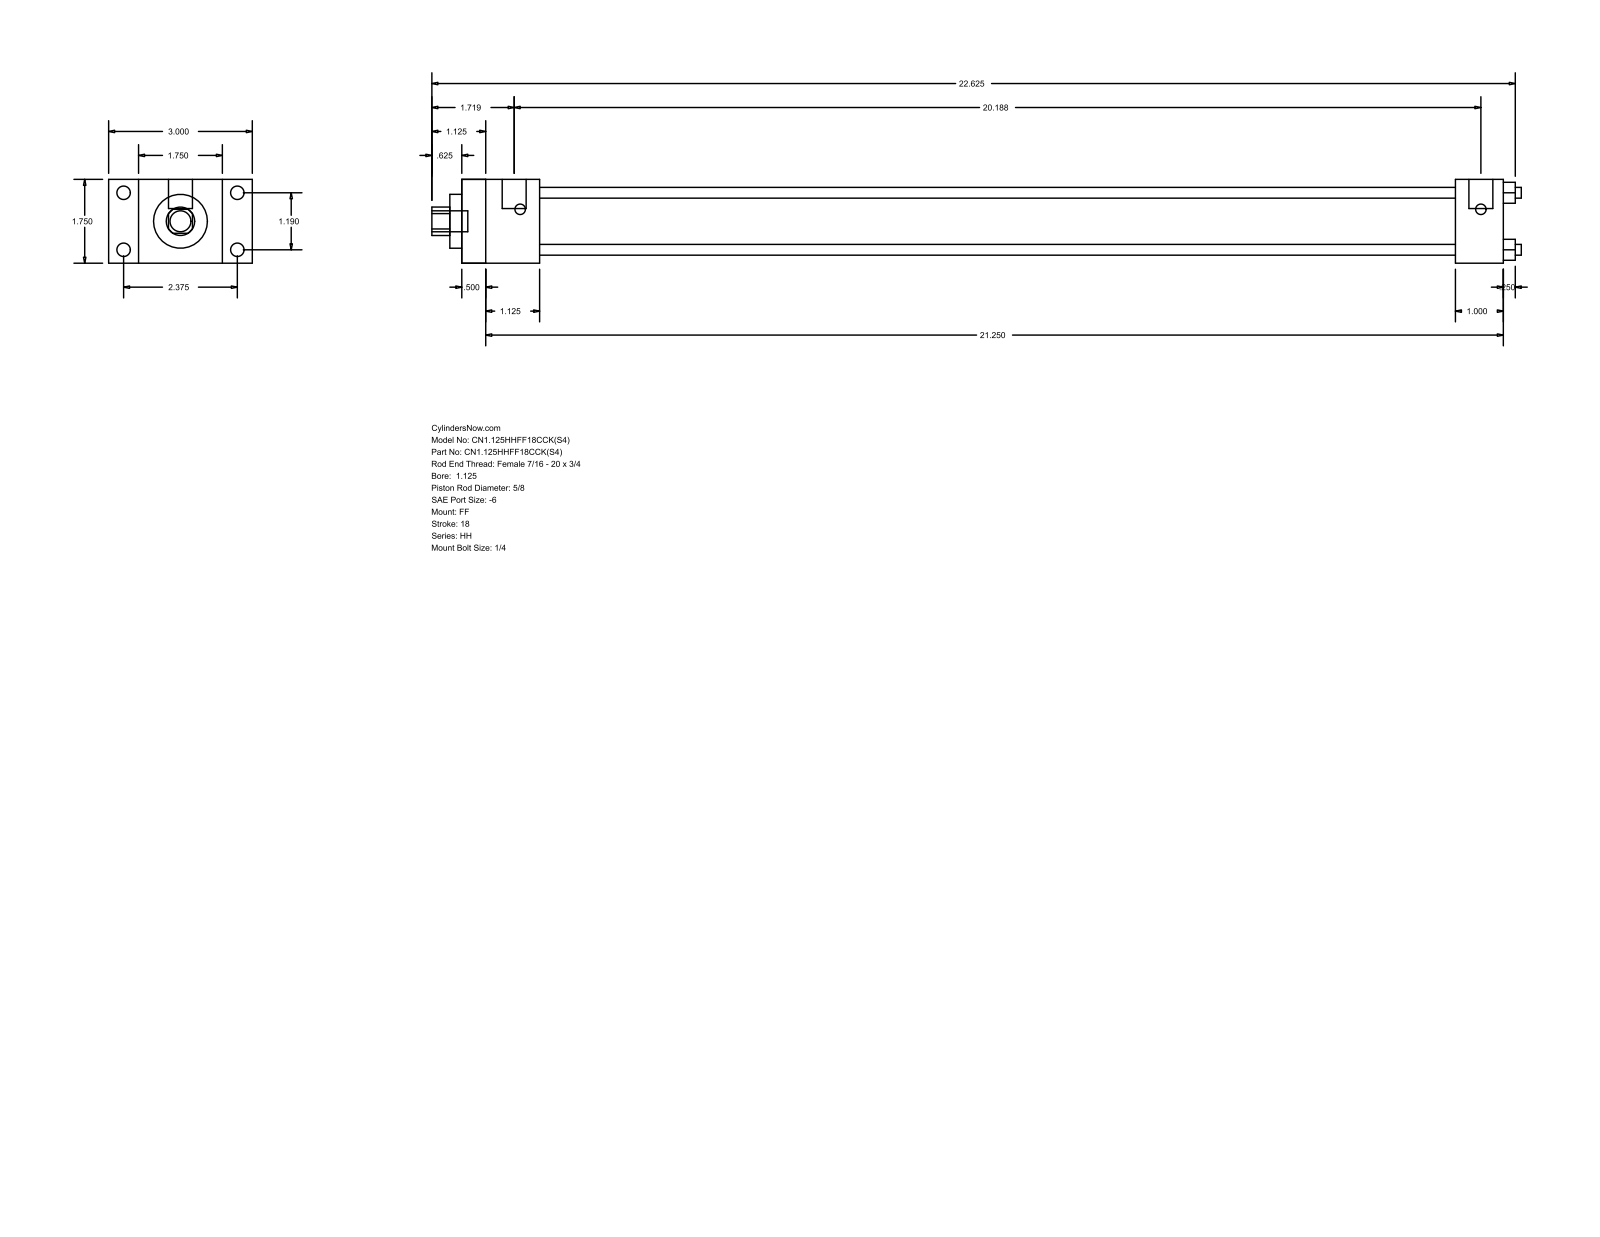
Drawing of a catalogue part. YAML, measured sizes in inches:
part_name: "HH_FF__0112_0.625"
step_written_by: "GSSL Pune (CONFIG_CONTROL_DESIGN)"
units: inches
bodies: {solids: 0, faces: 92, planar: 64, cylindrical: 28, other: 0}
overall_size: [22.75, 3, 1.75]
round_holes:
  - {diameter: 0.225, count: 4}
  - {diameter: 0.625, count: 1}
  - {diameter: 1.125, count: 1}
  - {diameter: 1.375, count: 1}
round_bosses_or_shafts:
  - {diameter: 0.281, count: 4}
  - {diameter: 0.219, count: 4}
  - {diameter: 0.5, count: 2}
  - {diameter: 0.437, count: 1}
partial_cylinders:
  - {radius: 0.297, count: 1}
face_to_face_distances: [1.75, 21.75, 0.5, 21.25, 0.625, 2.375, 1.125, 1.625, 20.75, 20.25]
hole_center_spacings: [0.841, 1.19, 1.683]
